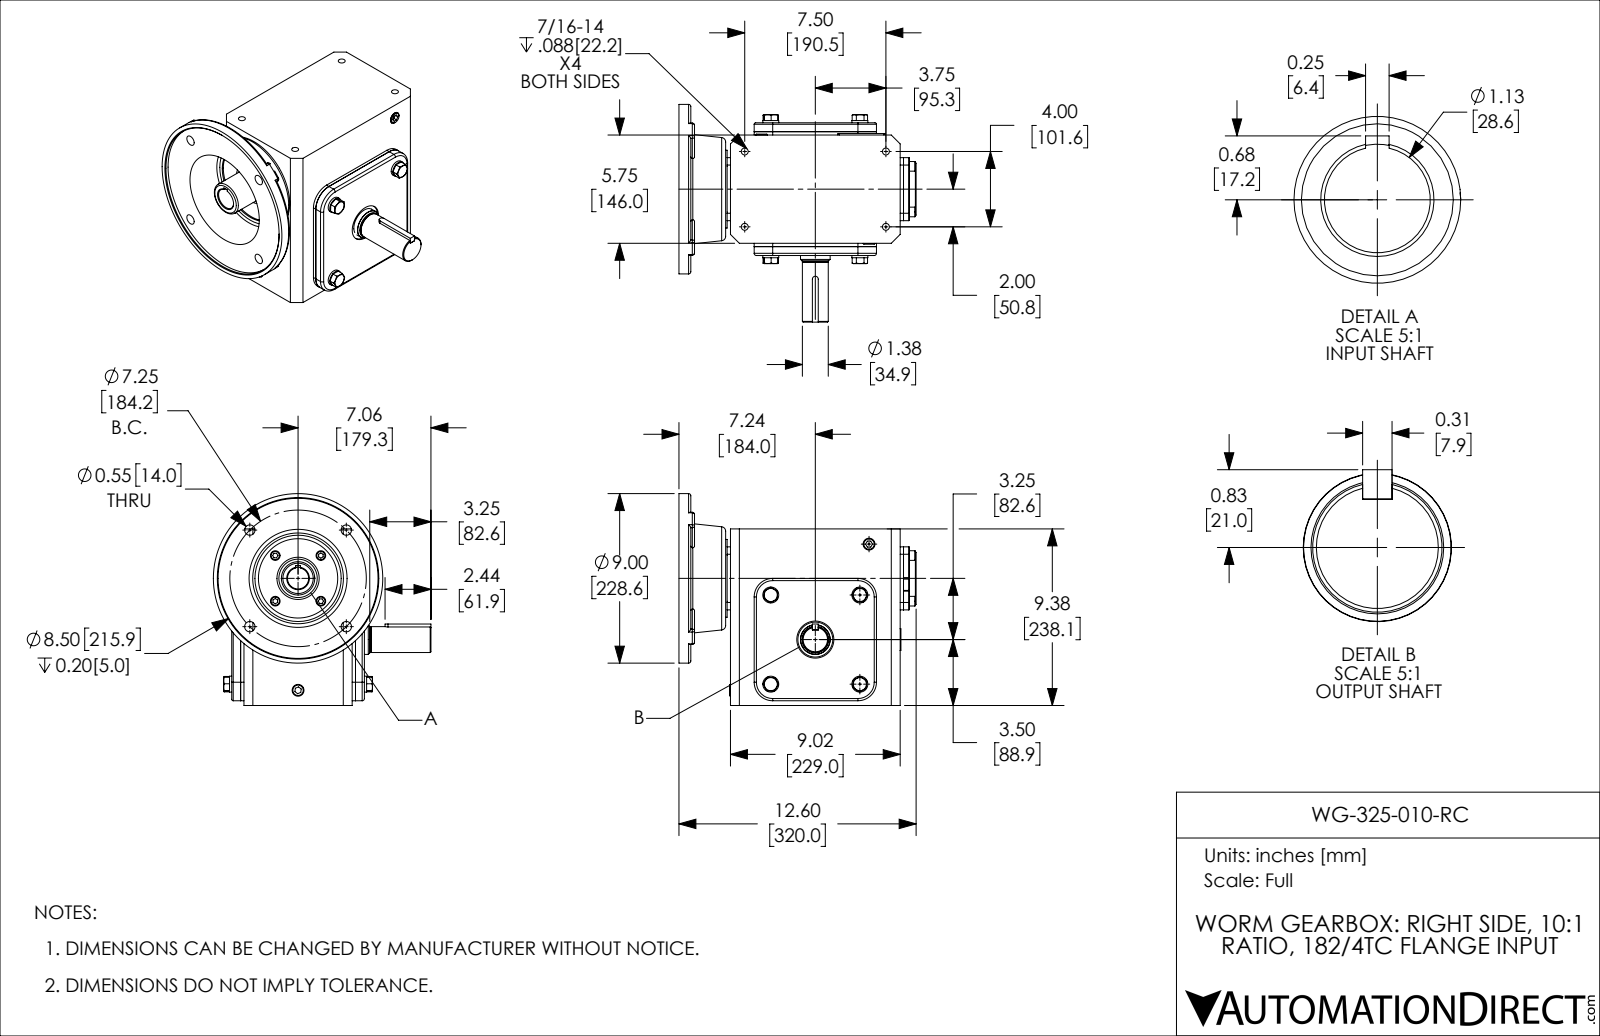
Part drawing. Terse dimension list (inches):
name: WG-325-010-RC
written by: SolidWorks 2017 (AUTOMOTIVE_DESIGN)
unit: in
bodies: 40 solids, 654 faces (336 planar, 196 cylindrical, 122 other)
size: 12.598 × 11.559 × 11.25
volume: 529.7 in³; area: 1 026 in²
holes: 4× ⌀0.354, 4× ⌀0.368, 4× ⌀0.551, 3× ⌀0.628, 1× ⌀0.591, 1× ⌀0.978, 1× ⌀1.125, 1× ⌀1.181, 1× ⌀1.969, 1× ⌀2.244, 1× ⌀2.441, 1× ⌀2.756
bosses: 4× ⌀0.846, 4× ⌀0.512, 1× ⌀9, 1× ⌀4.134, 1× ⌀2.835, 1× ⌀1.772, 1× ⌀1.575, 1× ⌀1.375
rounds: 14× R0.118, 11× R0.079, 4× R0.394, 4× R0.906, 4× R0.984, 2× R0.02, 2× R0.039, 1× R0.156
face distances: 0.079, 0.177, 6.496, 0.394, 6.969, 0.472, 6.575, 6.398, 0.571, 0.65
hole spacings: 4.009, 1.713, 1.913, 2.422, 3.625, 5.127, 5.338, 2.372
